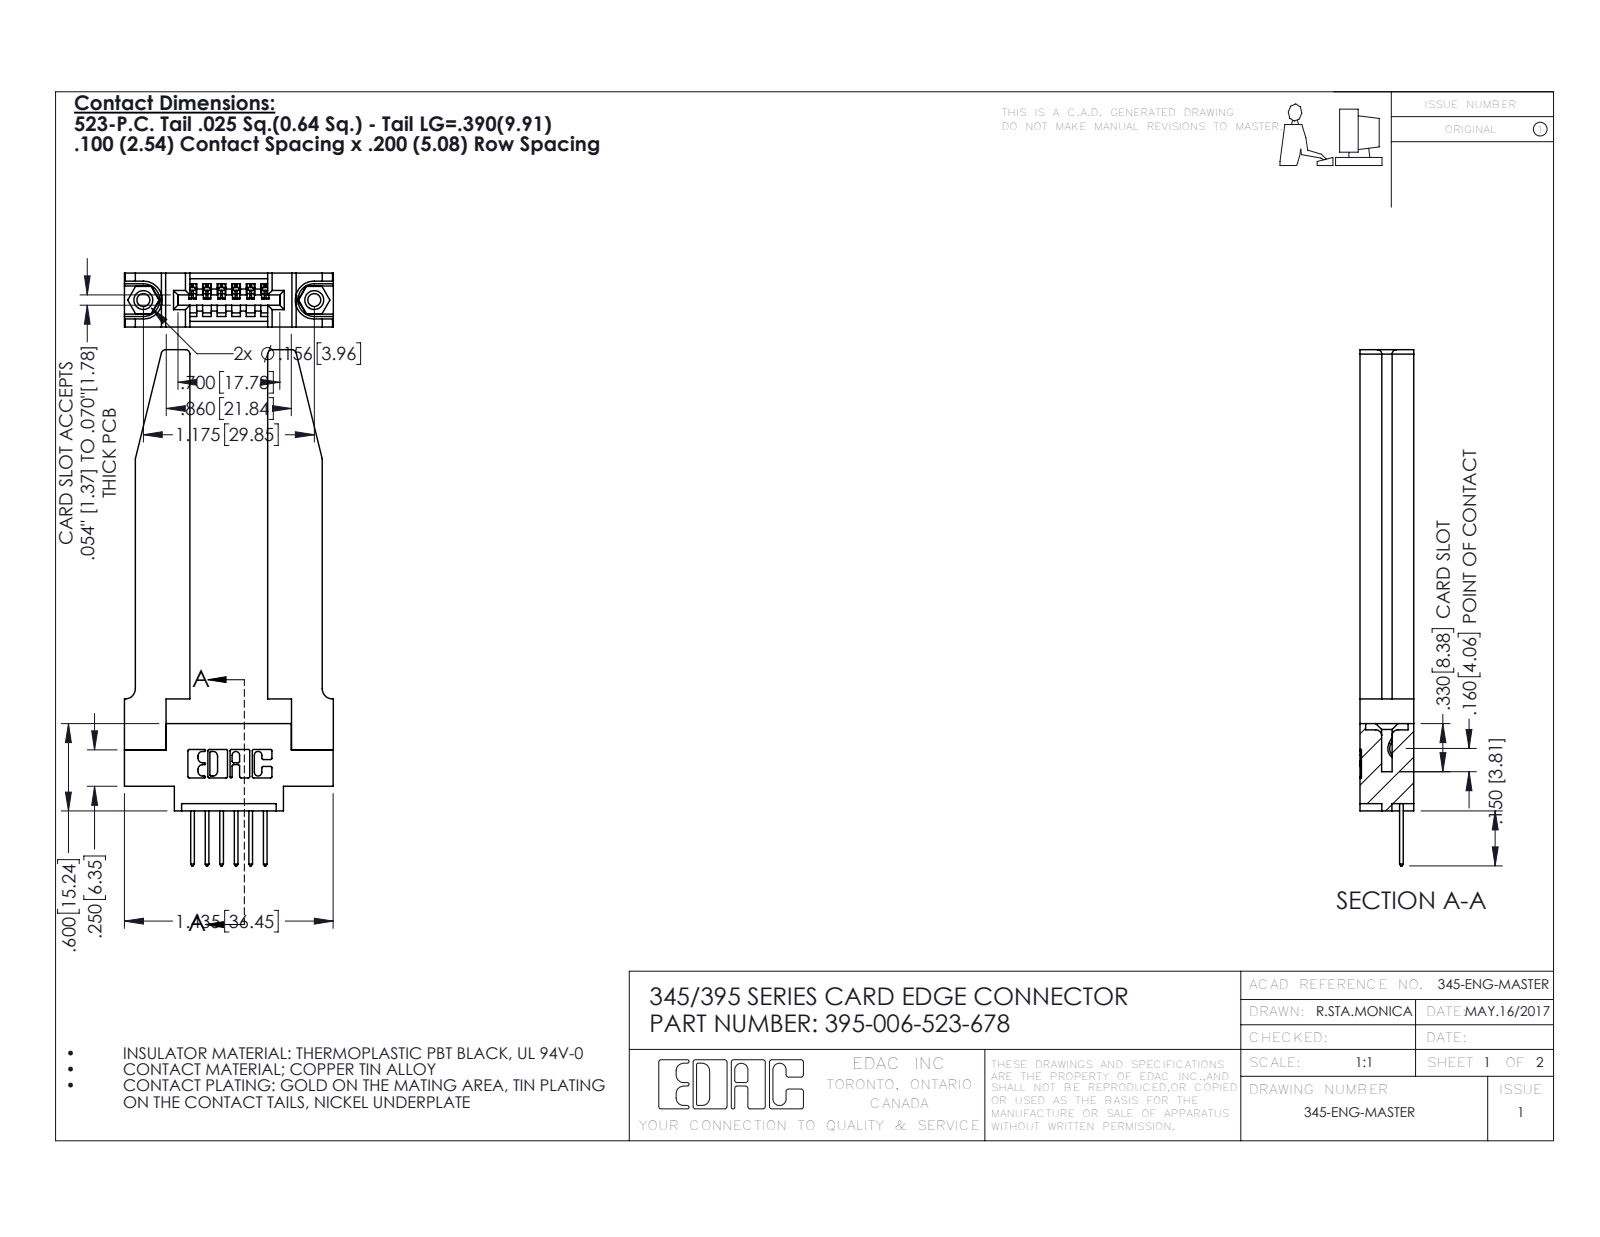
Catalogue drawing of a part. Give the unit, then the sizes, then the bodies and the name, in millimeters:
Units: millimetres
Overall size (bounding box): 90.1 × 36.5 × 9.4
Round holes (diameter × count): ⌀2.3 ×2, ⌀3.2 ×2, ⌀4 ×2, ⌀1.6 ×1
Round bosses / shafts (diameter × count): ⌀3.9 ×2
Partial cylindrical surfaces — rounded edges, fillets, slot ends (radius × count): R0.3 ×22, R0.2 ×12, R0.3 ×12, R0.8 ×8, R0.2 ×6, R0.8 ×6, R0.7 ×3, R0.8 ×2
Main face-to-face distances: 9.4, 3.8, 5.6, 13.6, 1.8, 3.8, 7.6, 2, 2.4, 1.8
Hole centre spacings: 6.9, 24, 29.8
Volume: 10 800 mm³ · Surface area: 10 550 mm²
Bodies: 11 solids, 712 faces (466 planar, 194 cylindrical, 52 other)
Part name (STEP PRODUCT): 345 Part_0.170 Offset - 0.156 Dia-TH; 395-006-523-678; 345-292-001_345-293-123; 345-250-001_345-250-001-102 (+1 more)
STEP written by: SolidWorks 2016 (CONFIG_CONTROL_DESIGN)
